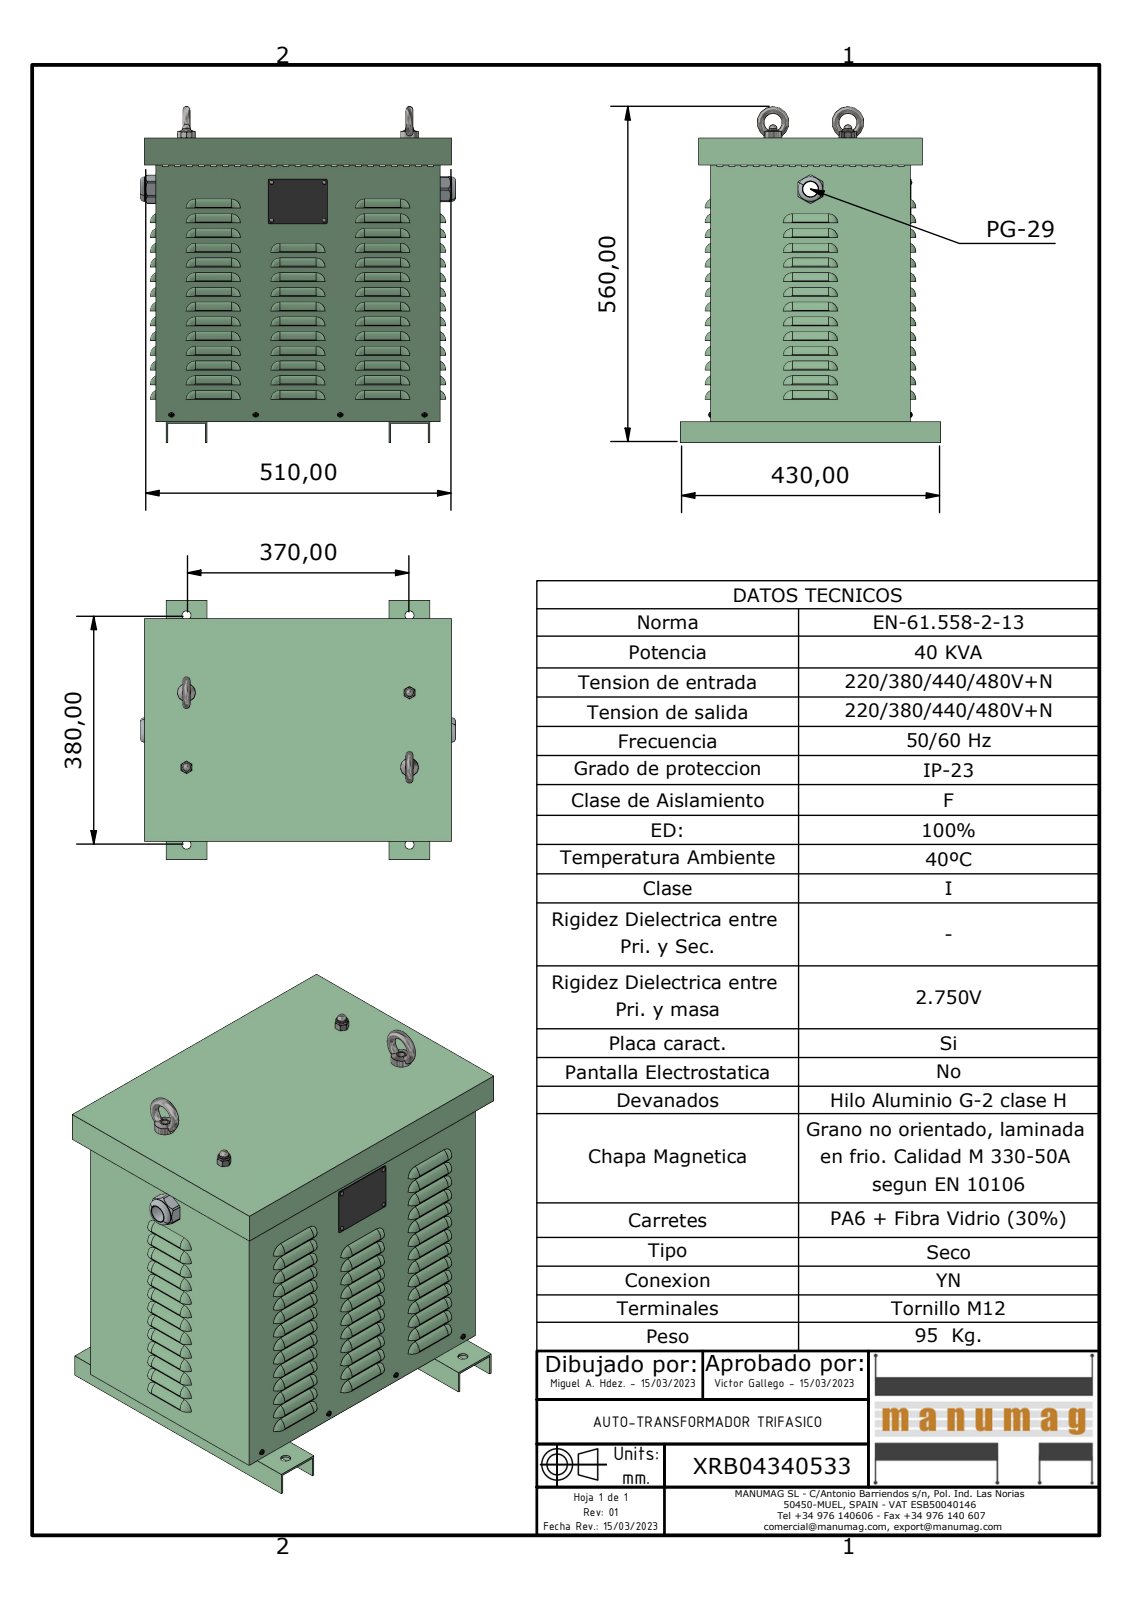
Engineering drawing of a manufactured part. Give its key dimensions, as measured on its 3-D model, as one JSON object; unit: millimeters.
{"part_name": "XRB04340533; JE040 - JE050 CUERPO; JE040 - JE050 BASE; JE040 - JE050 PATAS (+7 more)", "step_written_by": "Autodesk Inventor 2023 (AUTOMOTIVE_DESIGN)", "units": "millimeters", "bodies": {"solids": 24, "faces": 2403, "planar": 969, "cylindrical": 808, "other": 626}, "overall_size": [560, 523.4, 431], "volume_mm3": 3115000, "surface_area_mm2": 2768000, "round_holes": [[11, 260], [4, 4], [5, 4], [10.11, 4], [14, 4], [15, 4], [25, 1], [38, 1]], "round_bosses_or_shafts": [[4, 4], [3.62, 4], [3.2, 4], [30, 2], [18, 2], [13.6, 2], [40.8, 1], [37.3, 1]], "partial_cylinders_radius": [[14, 104], [7, 54], [15, 54], [3.22, 12], [2.5, 8], [7.5, 8], [2, 4], [23.85, 1]], "face_to_face_distances": [2, 470, 472, 329, 468, 327, 331, 3, 19.5, 348.5], "hole_center_spacings": [31.76, 71.59, 15, 28, 70, 44.6, 99.14, 140.8]}
